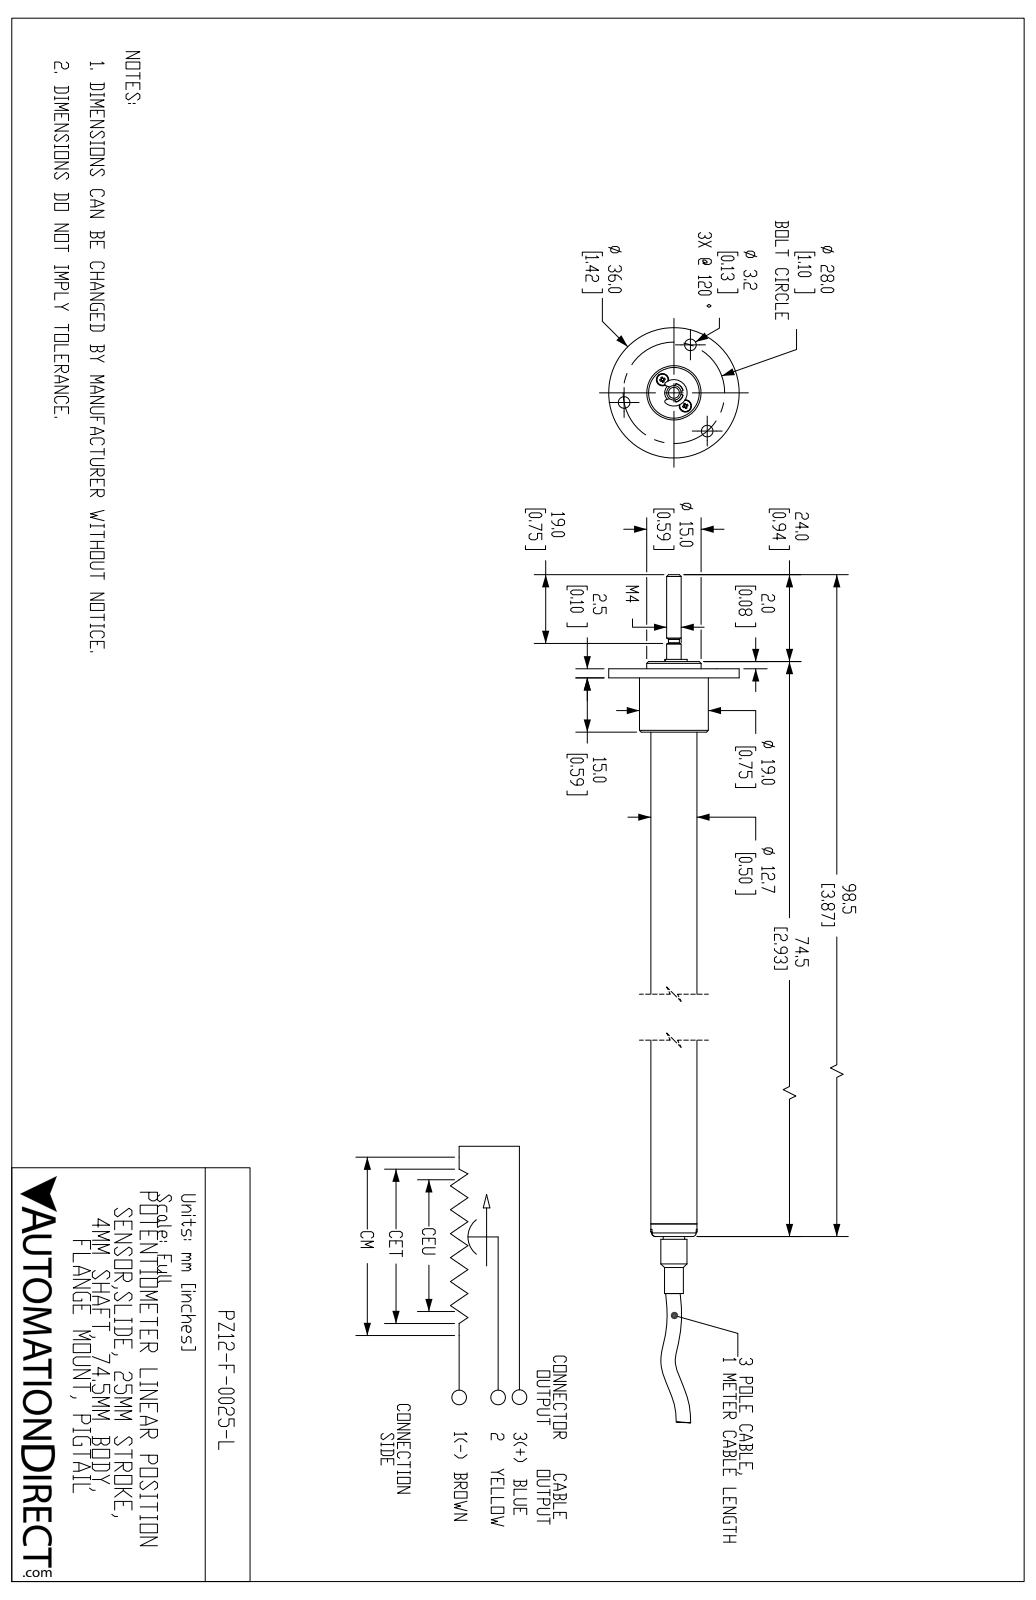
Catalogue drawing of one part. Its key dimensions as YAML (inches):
part_name: "PZ12-F-0025-L"
step_written_by: "SolidWorks 2019 (AUTOMOTIVE_DESIGN)"
units: inches
bodies: {solids: 11, faces: 489, planar: 129, cylindrical: 135, other: 225}
overall_size: [5.825, 1.417, 1.417]
volume: 0.93
surface_area: 16.07
round_holes:
  - {diameter: 0.126, count: 4}
  - {diameter: 0.055, count: 2}
  - {diameter: 0.079, count: 2}
  - {diameter: 0.134, count: 2}
  - {diameter: 0.039, count: 1}
  - {diameter: 0.138, count: 1}
  - {diameter: 0.201, count: 1}
  - {diameter: 0.236, count: 1}
  - {diameter: 0.502, count: 1}
round_bosses_or_shafts:
  - {diameter: 0.126, count: 4}
  - {diameter: 0.063, count: 4}
  - {diameter: 1.417, count: 1}
  - {diameter: 0.748, count: 1}
  - {diameter: 0.591, count: 1}
  - {diameter: 0.5, count: 1}
  - {diameter: 0.283, count: 1}
  - {diameter: 0.233, count: 1}
partial_cylinders:
  - {radius: 0.01, count: 4}
  - {radius: 0.02, count: 2}
  - {radius: 0.026, count: 2}
  - {radius: 0.069, count: 2}
  - {radius: 0.017, count: 1}
  - {radius: 0.103, count: 1}
  - {radius: 0.144, count: 1}
face_to_face_distances: [0.098, 2.539, 2.638, 0.079, 2.717, 0.177, 0.591, 1.949, 0.689, 0.768]
hole_center_spacings: [0.189, 0.551, 0.076, 0.37, 0.485, 0.666, 0.955, 0.362]
